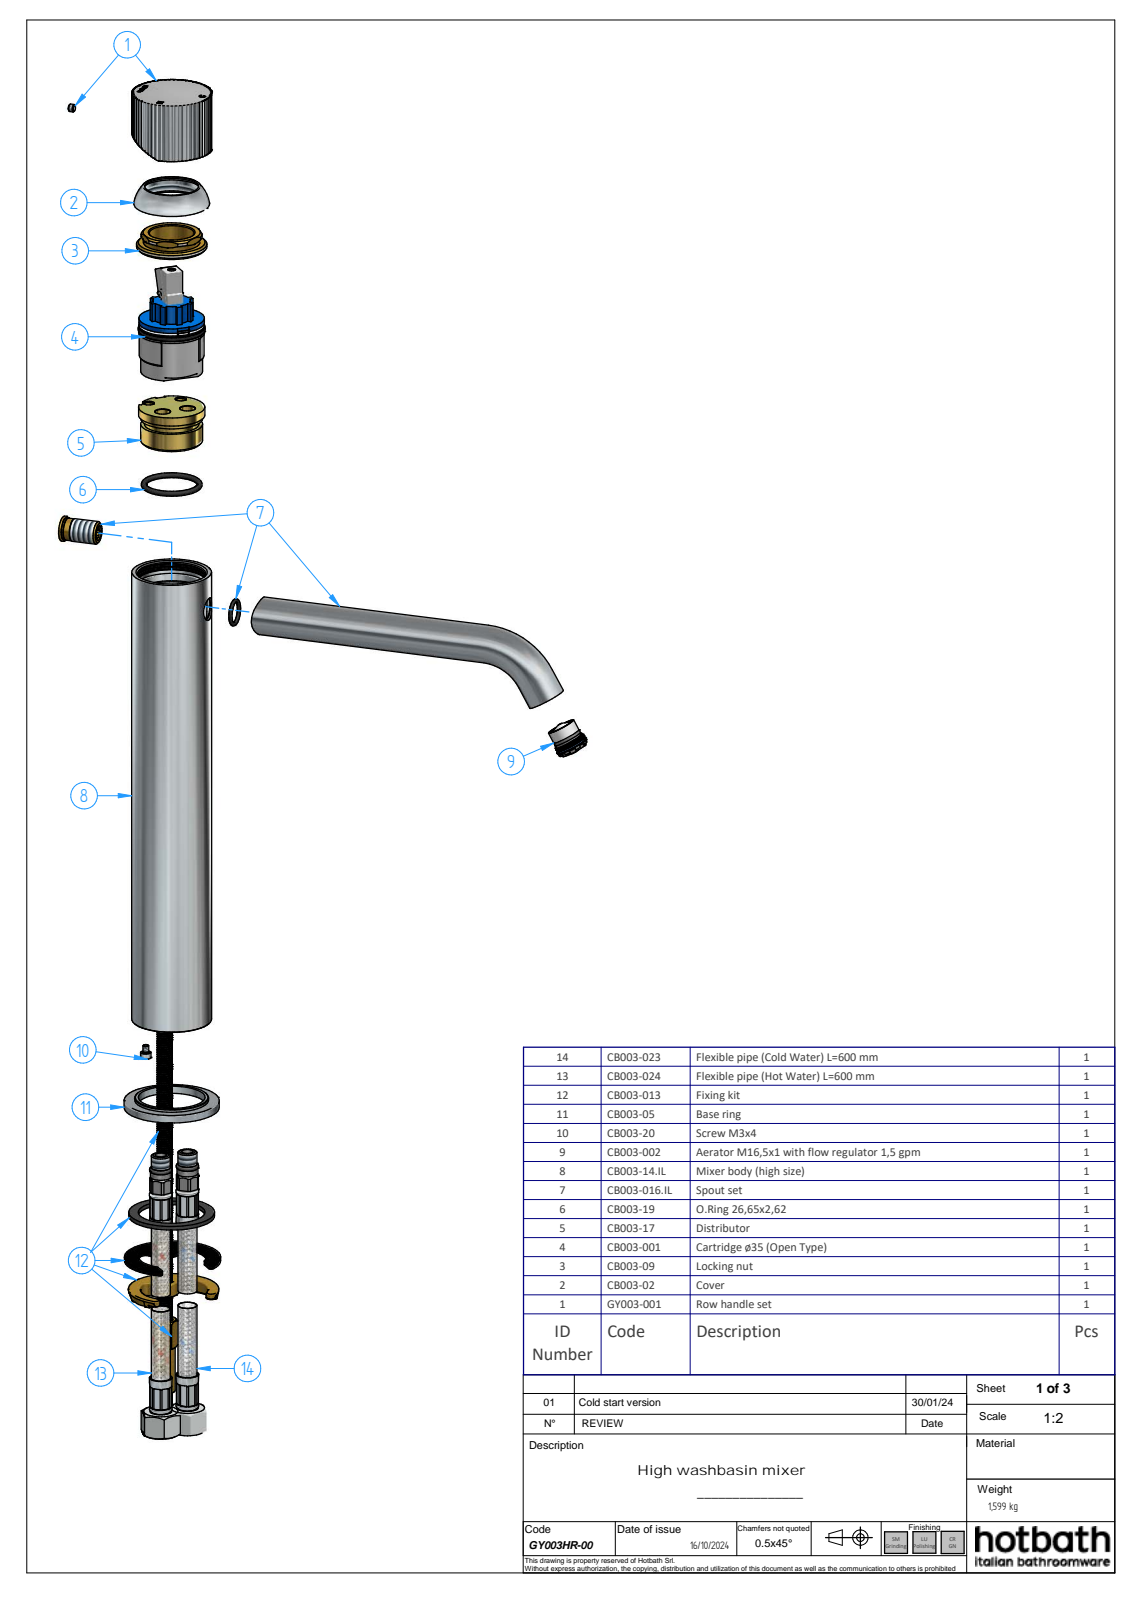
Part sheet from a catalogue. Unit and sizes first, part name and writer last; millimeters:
Units: millimetres
Overall size (bounding box): 285.5 × 213.92 × 50
Round holes (diameter × count): ⌀3.3 ×1, ⌀5 ×1, ⌀10.92 ×1, ⌀11 ×1, ⌀11.03 ×1, ⌀12 ×1, ⌀12.2 ×1, ⌀12.2 ×1, ⌀13.5 ×1, ⌀14 ×1, ⌀14.58 ×1, ⌀15.42 ×1
Round bosses / shafts (diameter × count): ⌀20 ×2, ⌀50 ×1, ⌀42 ×1, ⌀38.7 ×1, ⌀16.5 ×1, ⌀16 ×1, ⌀15.42 ×1, ⌀15.23 ×1
Partial cylindrical surfaces — rounded edges, fillets, slot ends (radius × count): R0.2 ×118, R0.1 ×60, R3 ×2, R0.49 ×1
Main face-to-face distances: 29, 279, 2.5, 281.5, 1.5, 4, 283, 253, 251.5, 249
Hole centre spacings: 34.5
Volume: 124 362 mm³ · Surface area: 101 473 mm²
Bodies: 9 solids, 1054 faces (283 planar, 301 cylindrical, 470 other)
Part name (STEP PRODUCT): GY003HR-00; CB003-14.IL; CB003-016.IL_oa_0; CB003-15.IL (+8 more)
STEP written by: Solid Edge (AUTOMOTIVE_DESIGN)
